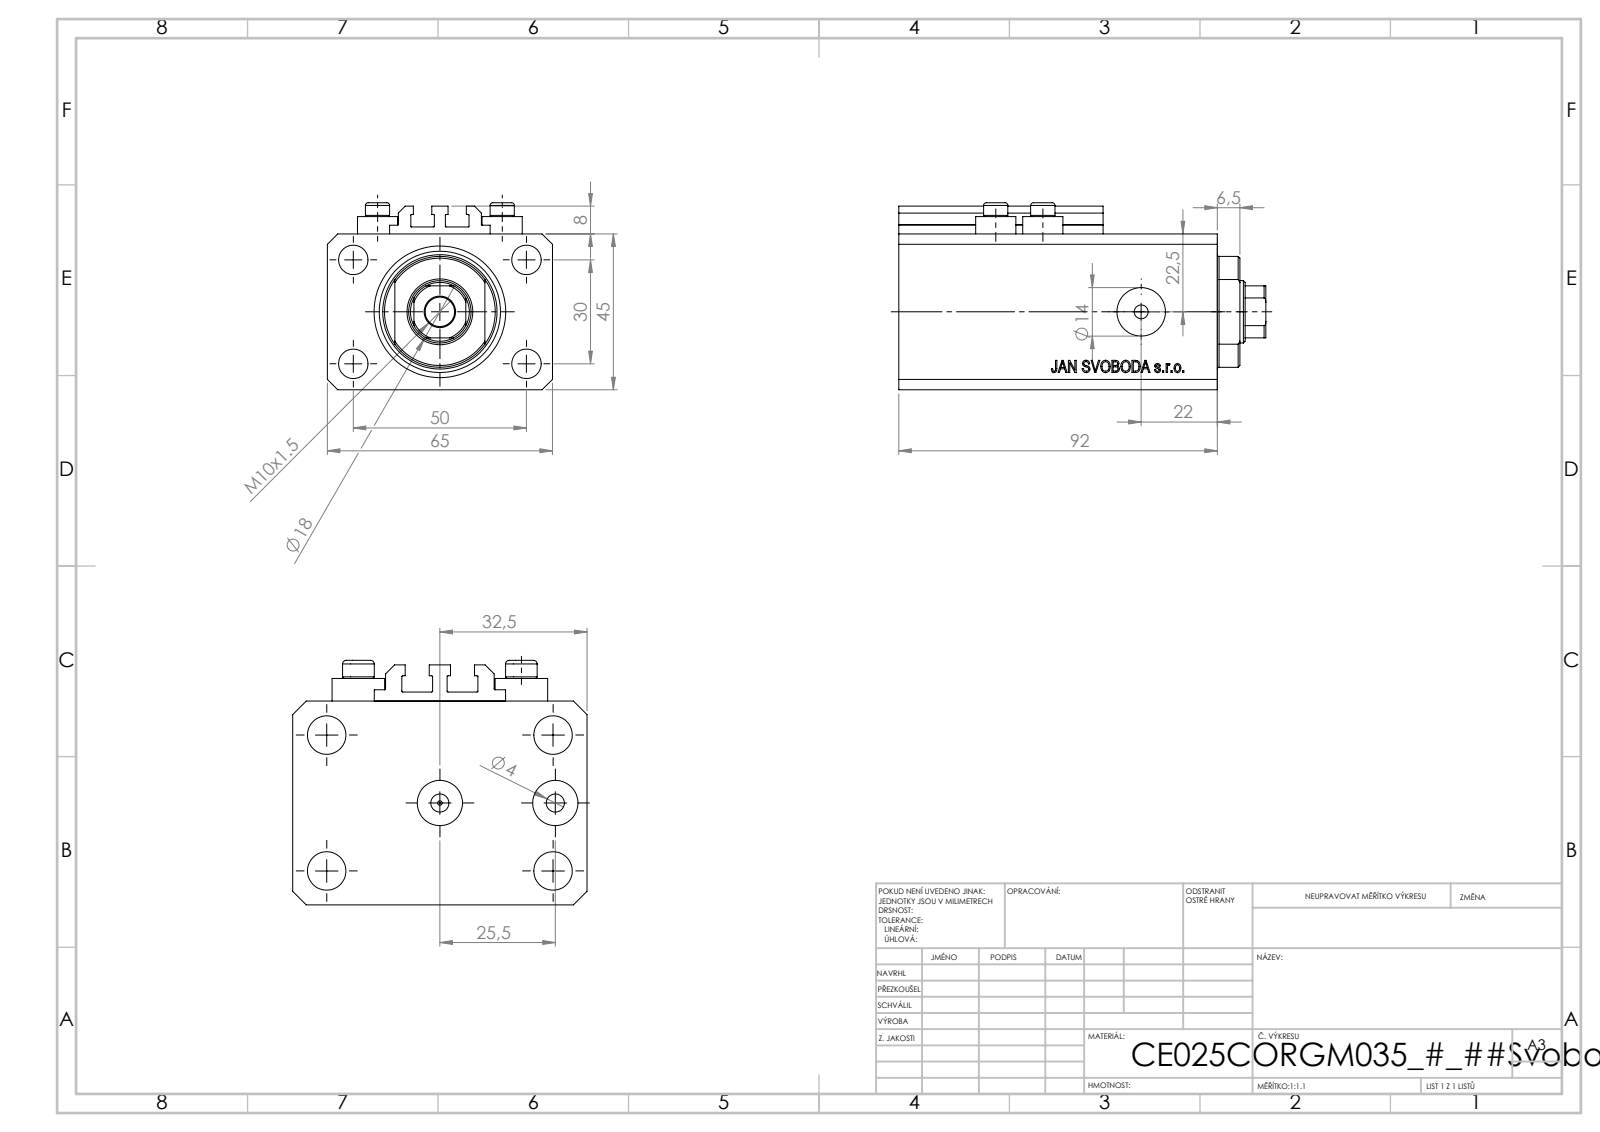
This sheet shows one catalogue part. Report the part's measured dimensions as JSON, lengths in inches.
{"part_name": "V250CE_VC_C; V250CE_C_VCP; V250CE_C_Body; ALLEN BOLT V250CE", "step_written_by": "SolidWorks 2019 (CONFIG_CONTROL_DESIGN)", "units": "inches", "bodies": {"solids": 8, "faces": 1038, "planar": 504, "cylindrical": 88, "other": 446}, "overall_size": [4.173, 2.559, 2.126], "volume_in3": 15.26, "surface_area_in2": 102.4, "round_holes": [[0.157, 8], [0.335, 5], [0.394, 2], [0.551, 2], [0.049, 1], [0.709, 1], [0.984, 1], [1.496, 1]], "round_bosses_or_shafts": [[0.457, 4], [0.276, 4]], "partial_cylinders_radius": [[0.008, 10], [0.335, 1], [0.63, 1]], "face_to_face_distances": [1.772, 2.559, 0.551, 3.622, 3.071, 1.85, 0.272, 2.799, 3.35, 0.118], "hole_center_spacings": [1.148, 0.535, 0.591, 1.181, 1.417, 1.515, 1.969, 2.074]}
